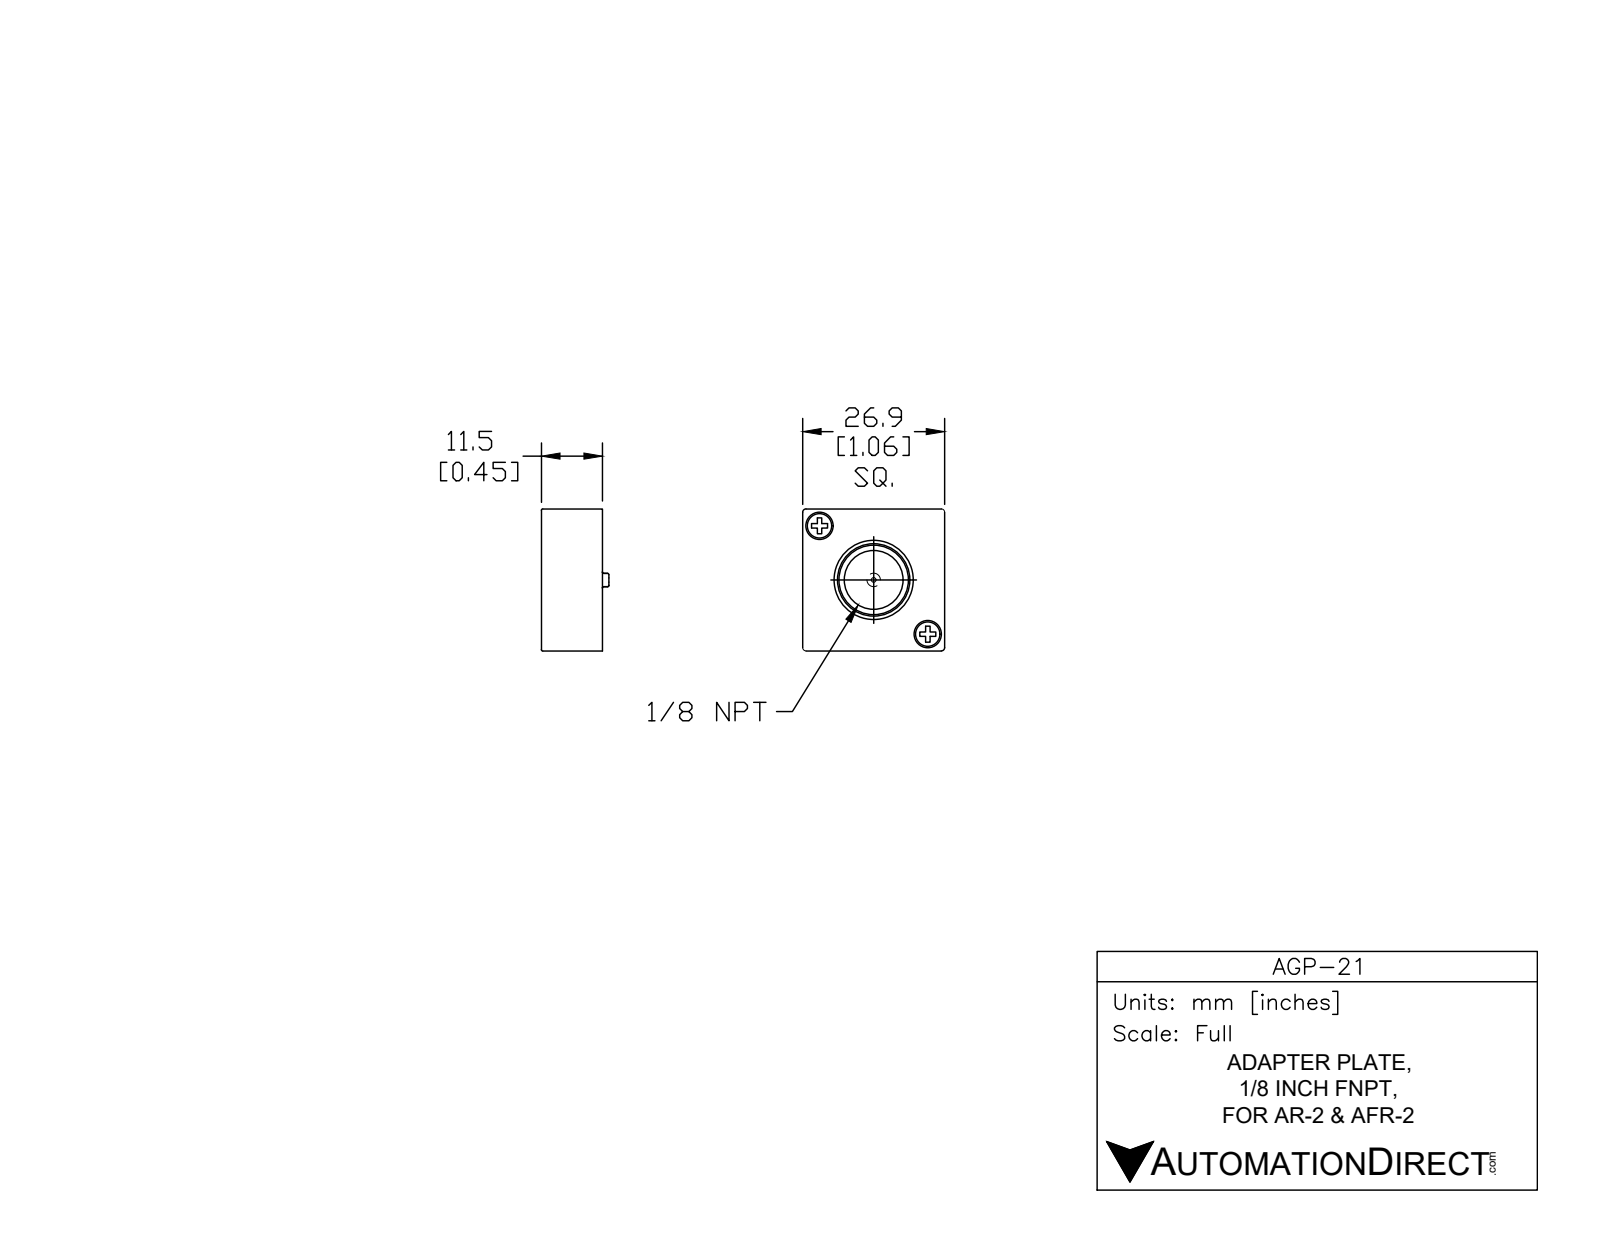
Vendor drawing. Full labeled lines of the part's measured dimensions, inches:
Part name (STEP PRODUCT): AGP-21
STEP written by: SolidWorks 2015 (CONFIG_CONTROL_DESIGN)
Units: inches
Bodies: 1 solid, 73 faces (39 planar, 22 cylindrical, 12 other)
Overall size (bounding box): 1.058 × 1.058 × 0.502
Volume: 0.461 in³ · Surface area: 4.85 in²
Round holes (diameter × count): ⌀0.203 ×2, ⌀0.035 ×1, ⌀0.332 ×1
Round bosses / shafts (diameter × count): ⌀0.181 ×2, ⌀0.1 ×1
Partial cylindrical surfaces — rounded edges, fillets, slot ends (radius × count): R0.01 ×4, R0.025 ×4
Main face-to-face distances: 1.058, 0.454, 0.079, 0.375, 0.424, 0.345, 0.03, 0.184, 0.105, 0.24
Hole centre spacings: 0.571, 1.141
